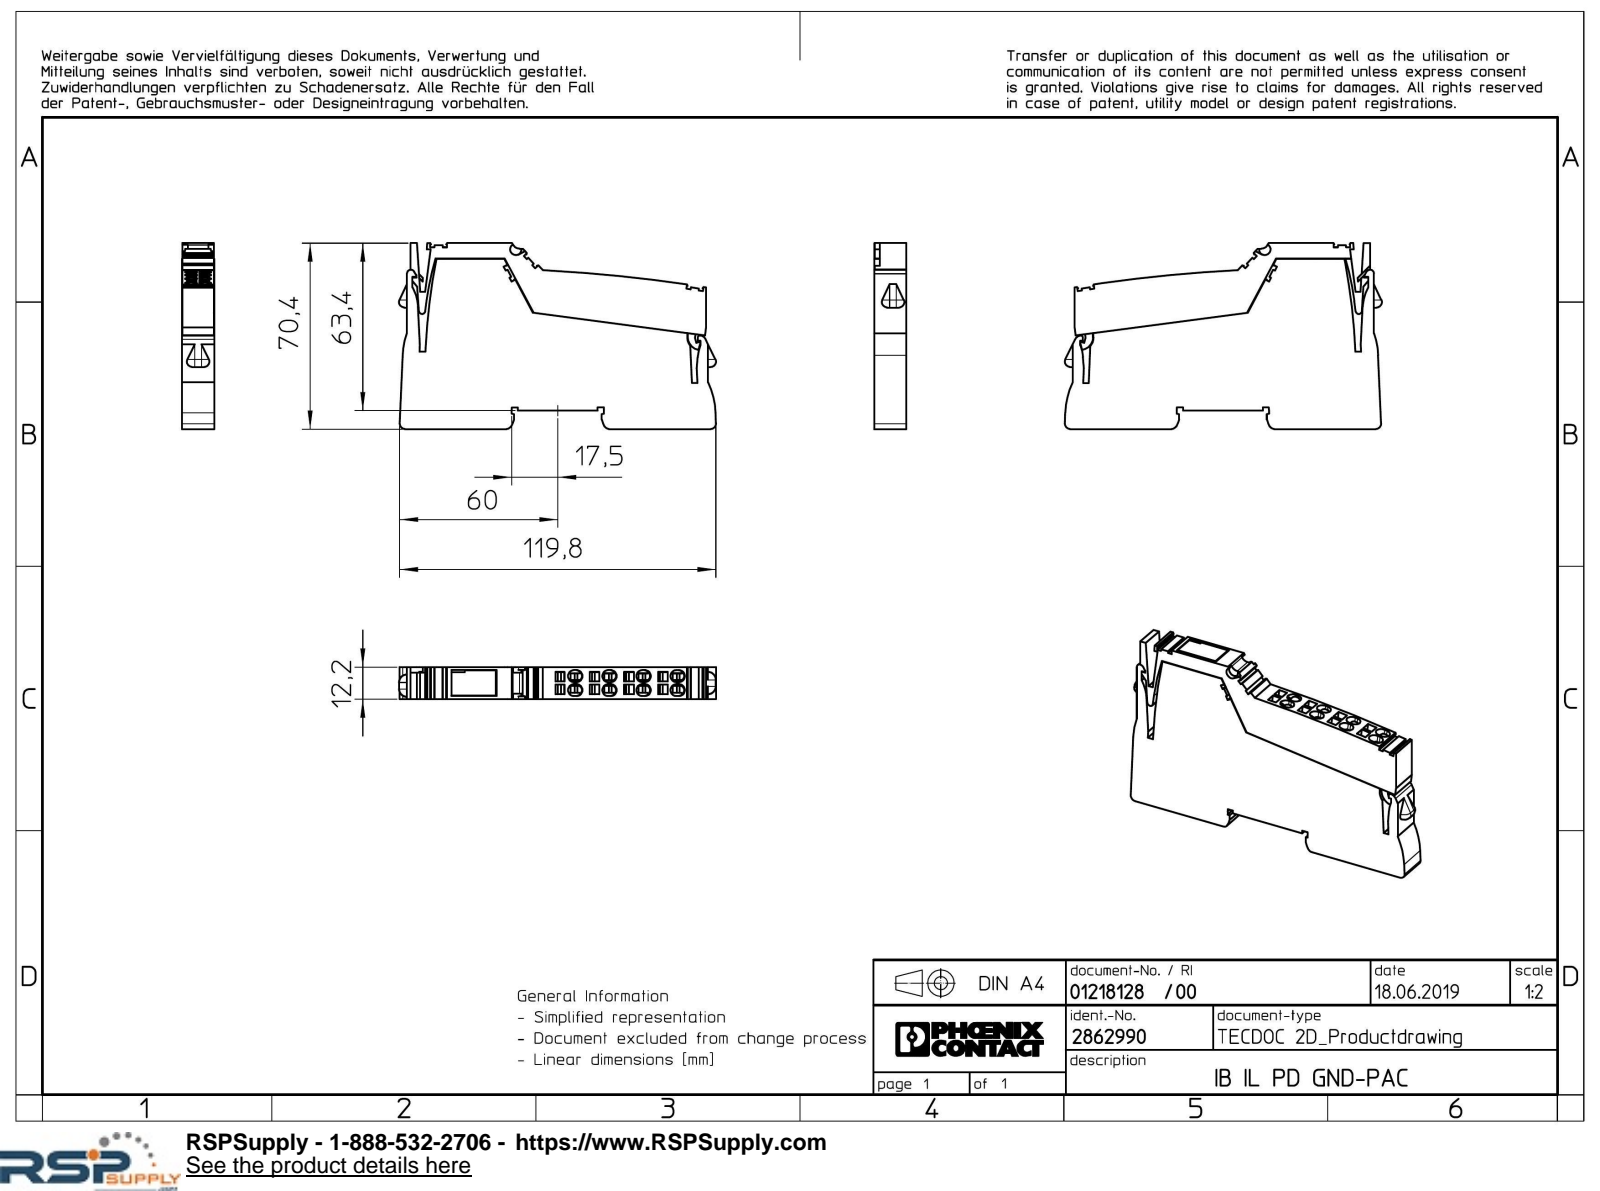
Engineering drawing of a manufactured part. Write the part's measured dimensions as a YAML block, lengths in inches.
part_name: "L-L_ST_GN_6021-select; L_L_2_GEH_GN_6021-select; L_L_LWL_BK_AUSSEN-select; IB_IL_PD_GND_PAC-select"
step_written_by: "Creo Elements/Direct Modeling 20.1A 29-Sep-2018 (C) Parametric Technology GmbH (AUTOMOTIVE_DESIGN)"
units: inches
bodies: {solids: 3, faces: 598, planar: 501, cylindrical: 61, other: 36}
overall_size: [4.729, 2.773, 0.478]
volume: 4.858
surface_area: 44.6
round_holes:
  - {diameter: 0.047, count: 6}
partial_cylinders:
  - {radius: 0.089, count: 16}
  - {radius: 0.079, count: 6}
  - {radius: 0.006, count: 2}
  - {radius: 0.024, count: 2}
  - {radius: 0.335, count: 2}
  - {radius: 0.374, count: 2}
  - {radius: 0.657, count: 2}
  - {radius: 1.181, count: 2}
face_to_face_distances: [0.478, 0.476, 0.474, 0.472, 1.023, 0.512, 0.13, 2.535, 0.511, 0.189]
hole_center_spacings: [0.512, 0.546, 0.189, 1.024, 1.041]
